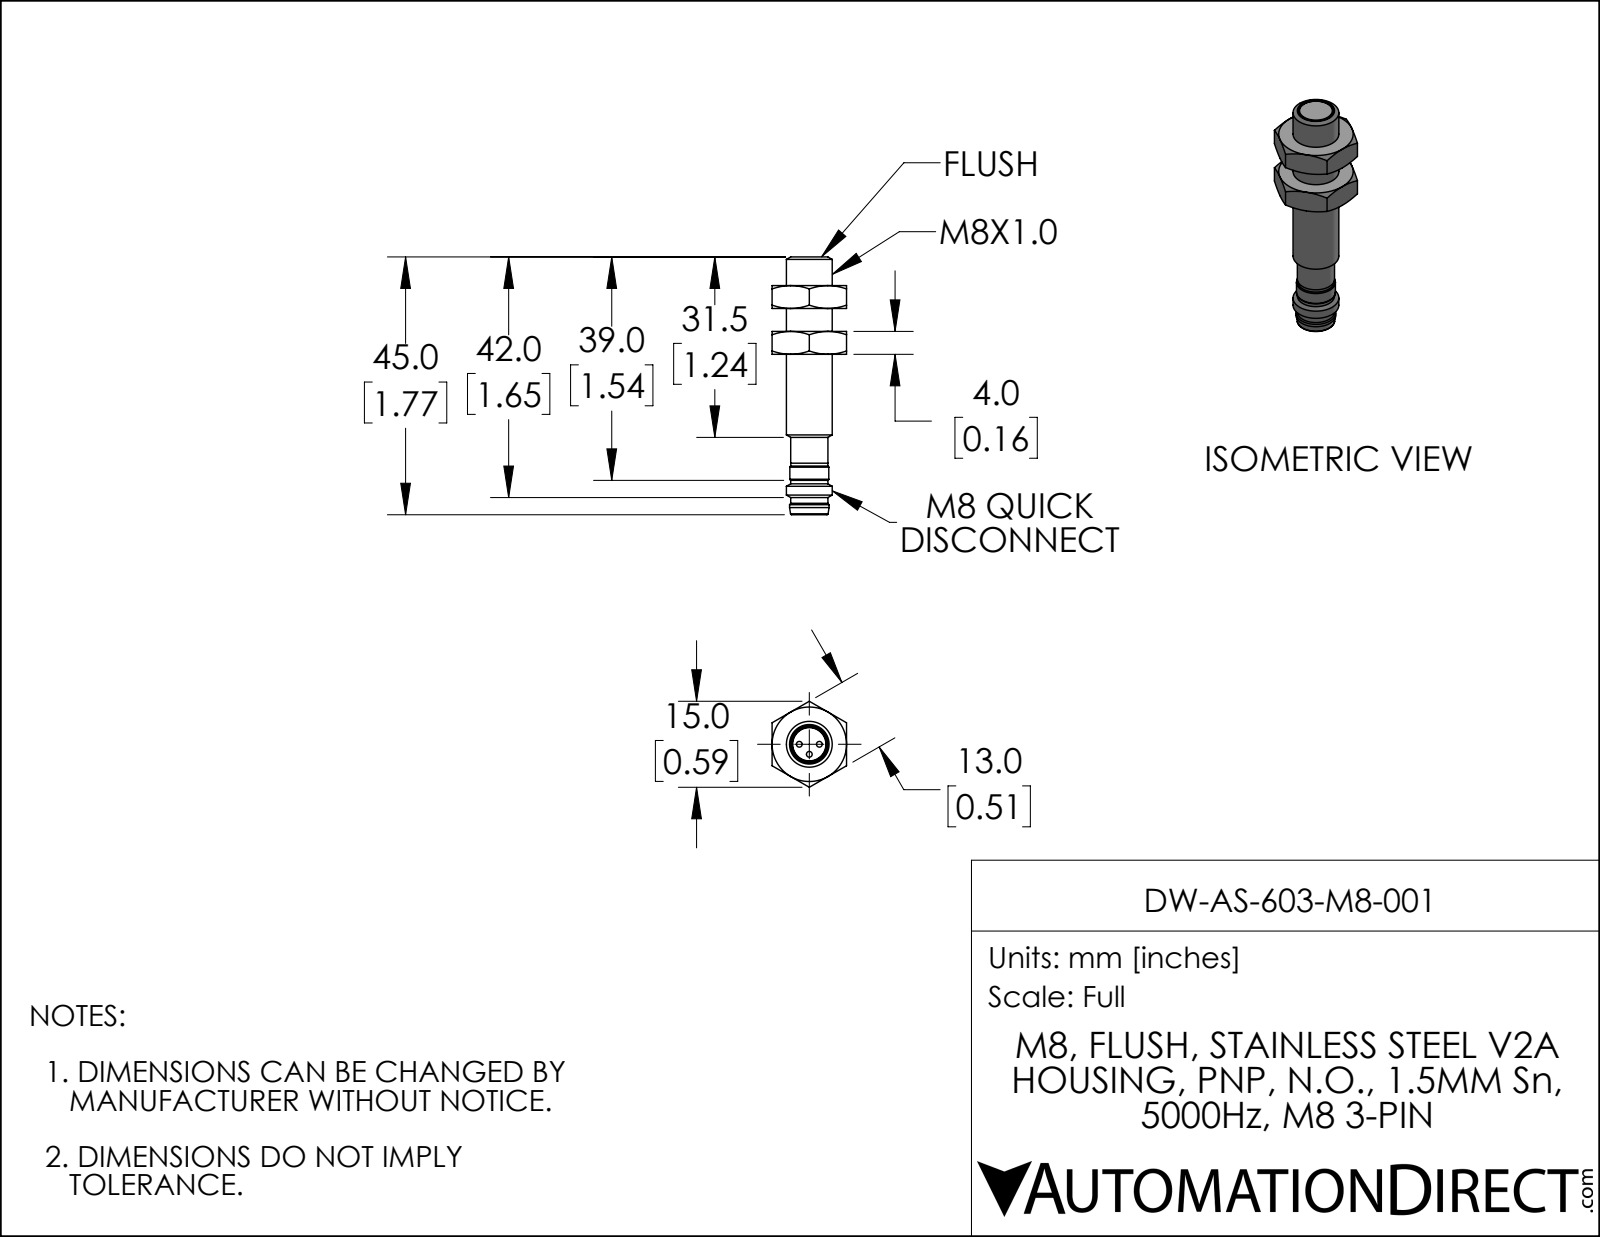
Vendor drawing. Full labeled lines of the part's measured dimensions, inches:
Part name (STEP PRODUCT): DW-AS-603-M8-001
STEP written by: SolidWorks 2019 (AUTOMOTIVE_DESIGN)
Units: inches
Bodies: 1 solid, 77 faces (25 planar, 14 cylindrical, 38 other)
Overall size (bounding box): 1.772 × 0.591 × 0.512
Volume: 0.165 in³ · Surface area: 2.85 in²
Round holes (diameter × count): ⌀0.228 ×1
Round bosses / shafts (diameter × count): ⌀0.039 ×3, ⌀0.315 ×1, ⌀0.272 ×1, ⌀0.268 ×1, ⌀0.256 ×1, ⌀0.254 ×1
Main face-to-face distances: 0.157, 0.512, 0.315, 0.472, 0.197, 0.354, 0.669, 1.575, 1.22, 1.063
